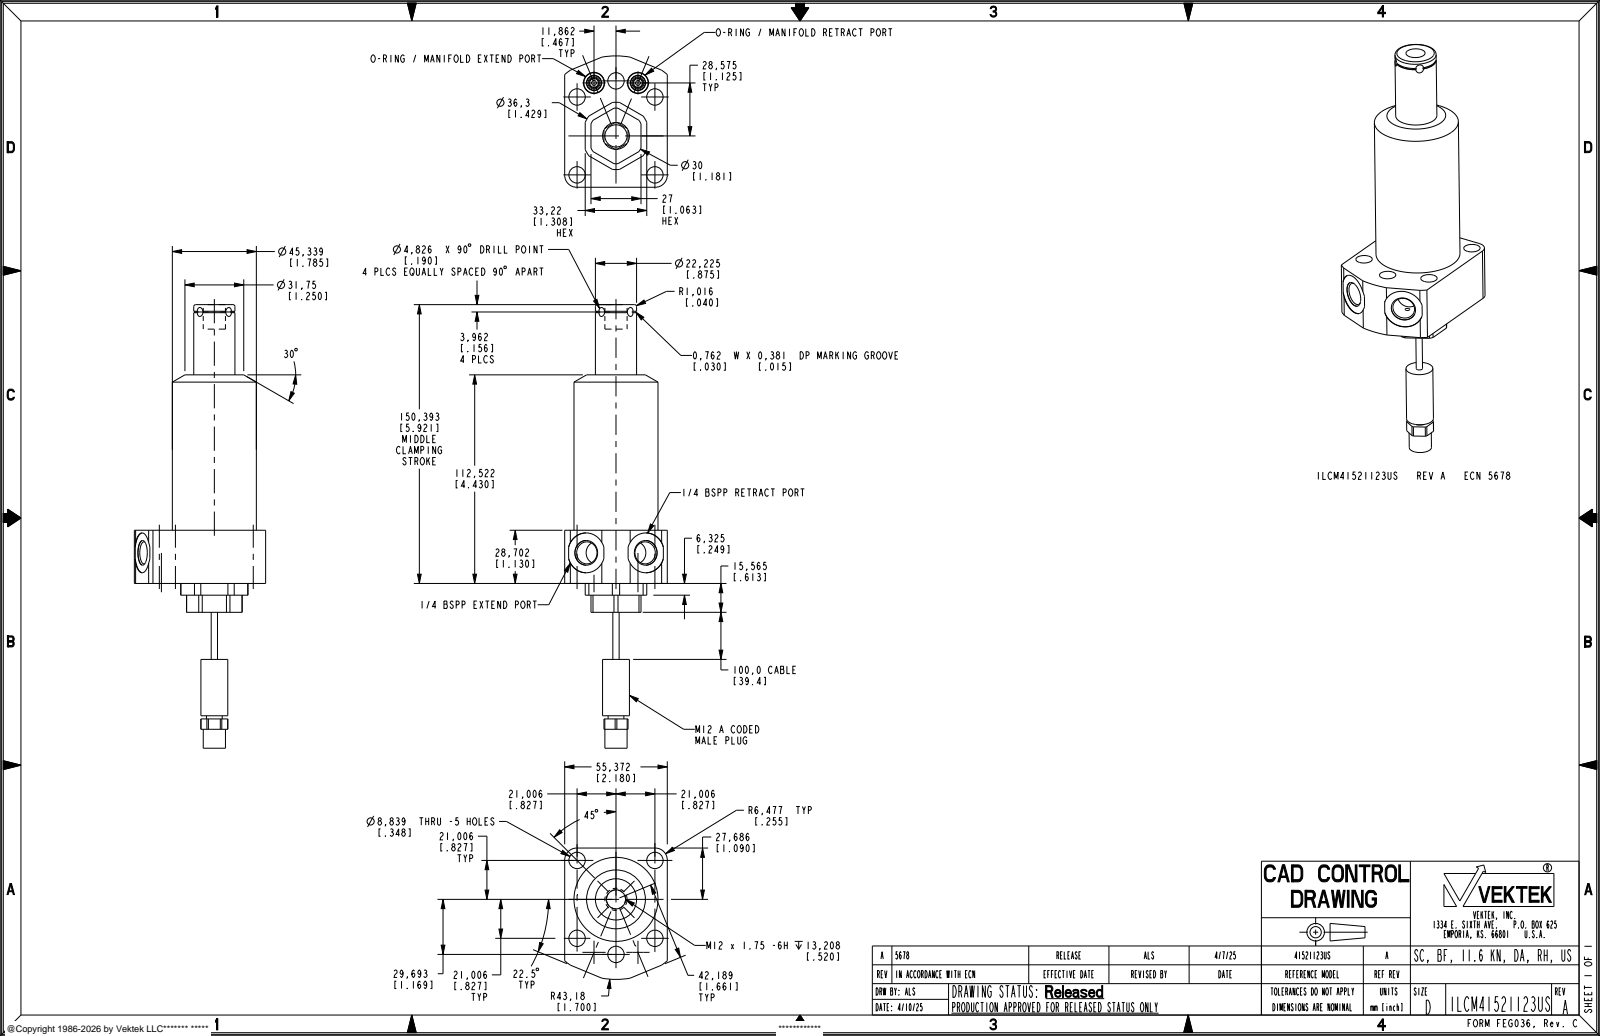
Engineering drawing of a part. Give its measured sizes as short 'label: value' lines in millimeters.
name: ILCM41521123US
written by: CREO PARAMETRIC BY PTC INC, 2021164 (AUTOMOTIVE_DESIGN)
unit: mm
bodies: 1 solid, 188 faces (75 planar, 83 cylindrical, 30 other)
size: 239.26 × 86.87 × 63.37
volume: 259 700 mm³; area: 38 865 mm²
holes: 5× ⌀8.84, 2× ⌀2.49, 2× ⌀6.5, 2× ⌀11.4, 2× ⌀11.89, 2× ⌀13.31, 2× ⌀21.5, 1× ⌀10.31
bosses: 2× ⌀5.49, 1× ⌀45.34, 1× ⌀22.23, 1× ⌀14.5, 1× ⌀11.99, 1× ⌀11.99, 1× ⌀8.51, 1× ⌀3.4
rounds: 2× R6.48, 1× R10.73, 1× R15, 1× R18.15, 1× R43.18
face distances: 28.7, 55.38, 15.57, 44.27, 3.11, 30.11, 128.09, 112.52, 83.82, 27
hole spacings: 29.71, 42.02, 11.87, 11.91, 22.73, 30.93, 33.73, 50.42
